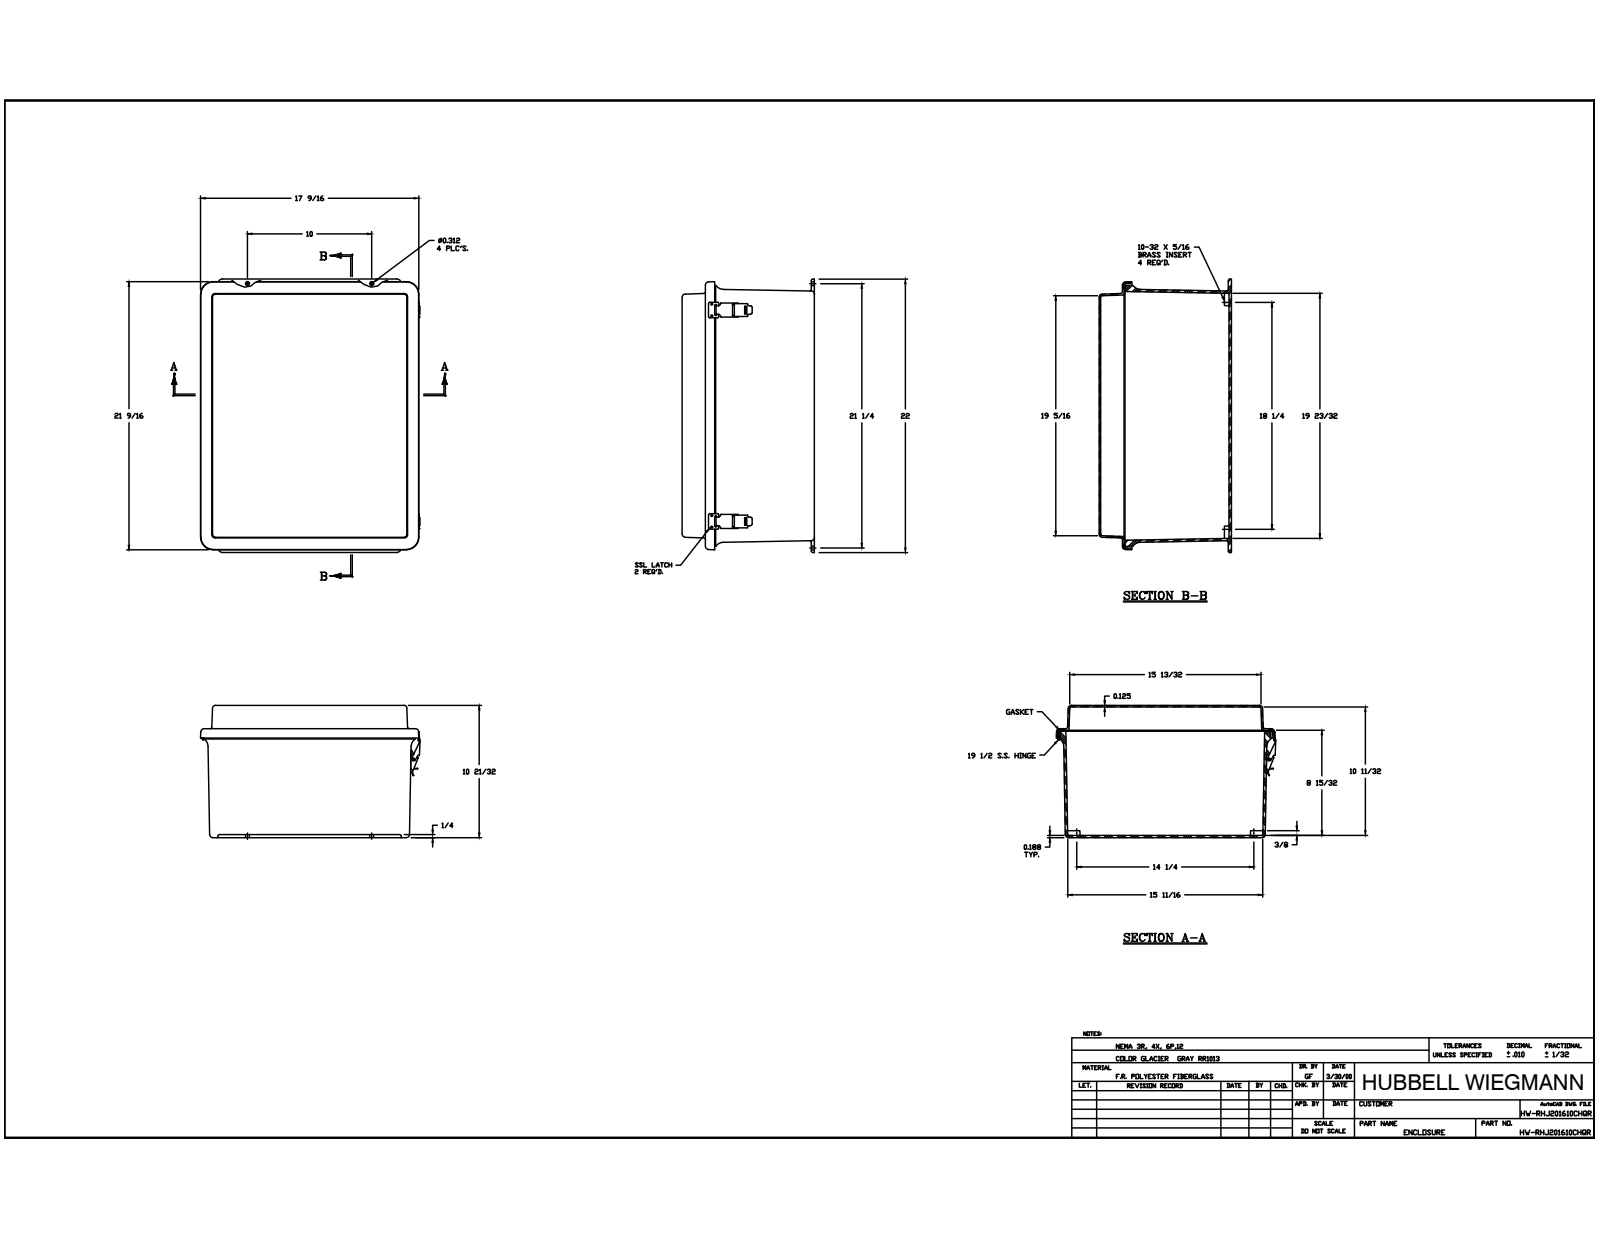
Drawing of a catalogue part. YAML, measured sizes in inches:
part_name: "J2016HL_1; RMINS45821P_1; RMINS45821P_2; RMINS45821P_3 (+8 more)"
step_written_by: "Autodesk Inventor 2014 (AUTOMOTIVE_DESIGN)"
units: inches
bodies: {solids: 42, faces: 1215, planar: 543, cylindrical: 505, other: 167}
overall_size: [22, 17.698, 10.642]
volume: 271.3
surface_area: 3191
round_holes:
  - {diameter: 0.14, count: 24}
  - {diameter: 0.131, count: 12}
  - {diameter: 0.104, count: 8}
  - {diameter: 0.152, count: 5}
  - {diameter: 0.13, count: 4}
  - {diameter: 0.156, count: 4}
  - {diameter: 0.218, count: 4}
  - {diameter: 0.135, count: 2}
  - {diameter: 0.375, count: 2}
  - {diameter: 0.085, count: 1}
round_bosses_or_shafts:
  - {diameter: 0.125, count: 20}
  - {diameter: 0.25, count: 12}
  - {diameter: 0.27, count: 4}
  - {diameter: 0.3, count: 1}
  - {diameter: 0.17, count: 1}
  - {diameter: 0.155, count: 1}
  - {diameter: 0.12, count: 1}
partial_cylinders:
  - {radius: 0.125, count: 30}
  - {radius: 0.015, count: 20}
  - {radius: 0.031, count: 20}
  - {radius: 0.045, count: 16}
  - {radius: 0.03, count: 12}
  - {radius: 0.25, count: 12}
  - {radius: 0.022, count: 9}
  - {radius: 0.06, count: 6}
face_to_face_distances: [0.187, 0.125, 0.188, 10.517, 10.642, 10.329, 10.454, 8.642, 8.454, 1.875]
hole_center_spacings: [3.75, 17, 7.5, 0.937, 0.25, 3.5, 4, 7.25]
